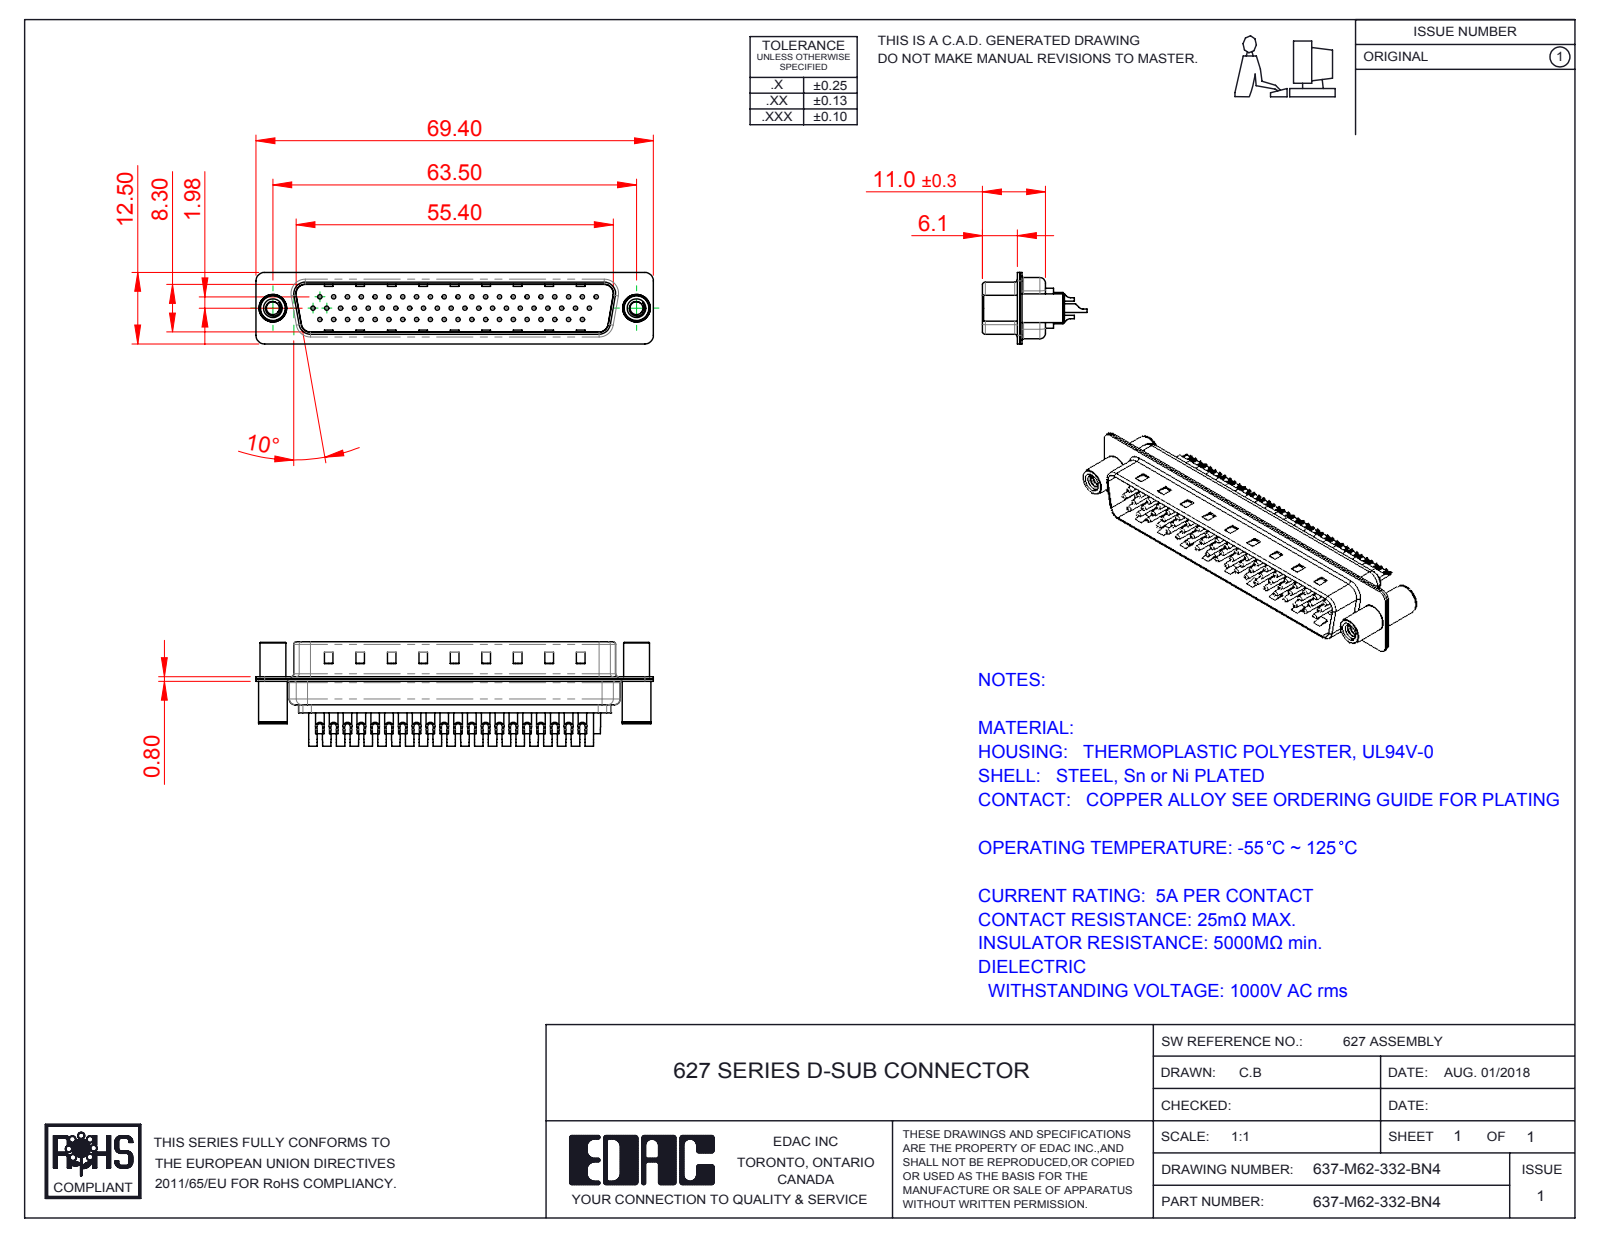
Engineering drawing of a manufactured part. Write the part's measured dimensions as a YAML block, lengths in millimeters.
part_name: "637M Shell Rear_62 Contacts; 637M Contact Row 3_32; 637M Contact Row 1_32; 637M 4-40 Threaded Standoff and Board Spacer (+4 more)"
step_written_by: "SolidWorks 2016 (CONFIG_CONTROL_DESIGN)"
units: millimeters
bodies: {solids: 67, faces: 2792, planar: 767, cylindrical: 1185, other: 840}
overall_size: [69.4, 18.25, 12.5]
volume: 4409
surface_area: 12706
round_holes:
  - {diameter: 0.75, count: 62}
  - {diameter: 1, count: 62}
  - {diameter: 1.6, count: 62}
  - {diameter: 2, count: 62}
  - {diameter: 2.26, count: 2}
  - {diameter: 3.26, count: 2}
  - {diameter: 4, count: 2}
  - {diameter: 4.8, count: 2}
round_bosses_or_shafts:
  - {diameter: 1.5, count: 62}
  - {diameter: 5, count: 2}
  - {diameter: 4.9, count: 2}
  - {diameter: 4.5, count: 2}
partial_cylinders:
  - {radius: 1.5, count: 16}
  - {radius: 2, count: 12}
  - {radius: 0.5, count: 8}
  - {radius: 1.6, count: 8}
  - {radius: 1, count: 7}
  - {radius: 0.25, count: 4}
  - {radius: 0.6, count: 4}
  - {radius: 0.65, count: 4}
face_to_face_distances: [0.4, 0.8, 9.5, 9.1, 8.7, 9.9, 0.75, 0.35, 1.2, 1.5]
hole_center_spacings: [7.24, 2.32, 2.41, 4.13, 9.65, 4.83, 14.48, 11.04]
